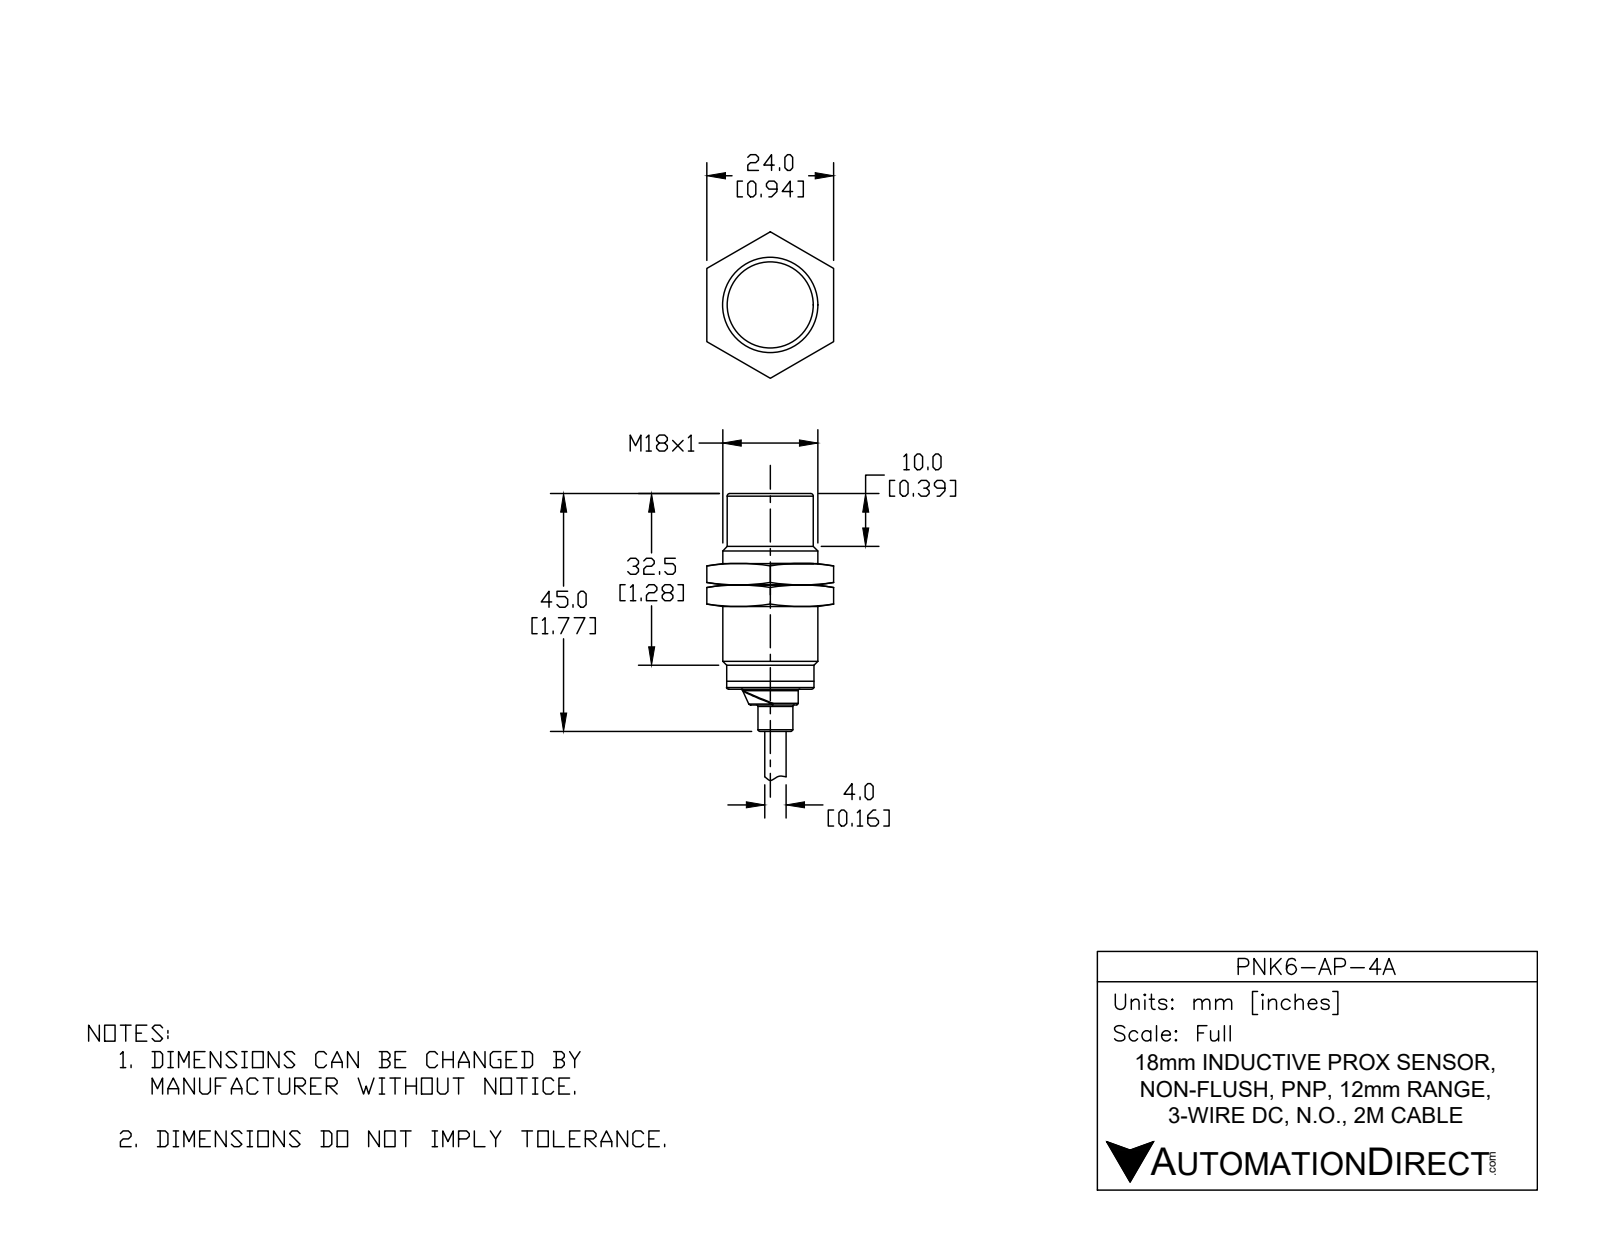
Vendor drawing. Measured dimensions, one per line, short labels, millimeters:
name: PNK6-AP-4A
written by: SolidWorks 2017 (AUTOMOTIVE_DESIGN)
unit: mm
bodies: 1 solid, 78 faces (19 planar, 27 cylindrical, 32 other)
size: 83.1 × 18 × 18
volume: 10 000 mm³; area: 3 500 mm²
holes: 1× ⌀4.1
bosses: 6× ⌀1.2, 1× ⌀18, 1× ⌀16.5, 1× ⌀16.5, 1× ⌀10.6, 1× ⌀6.6, 1× ⌀4
rounds: 1× R3.7
face distances: 37, 35.5, 1.5, 40, 4.5, 3, 39.2, 3.8, 2.3, 0.8
